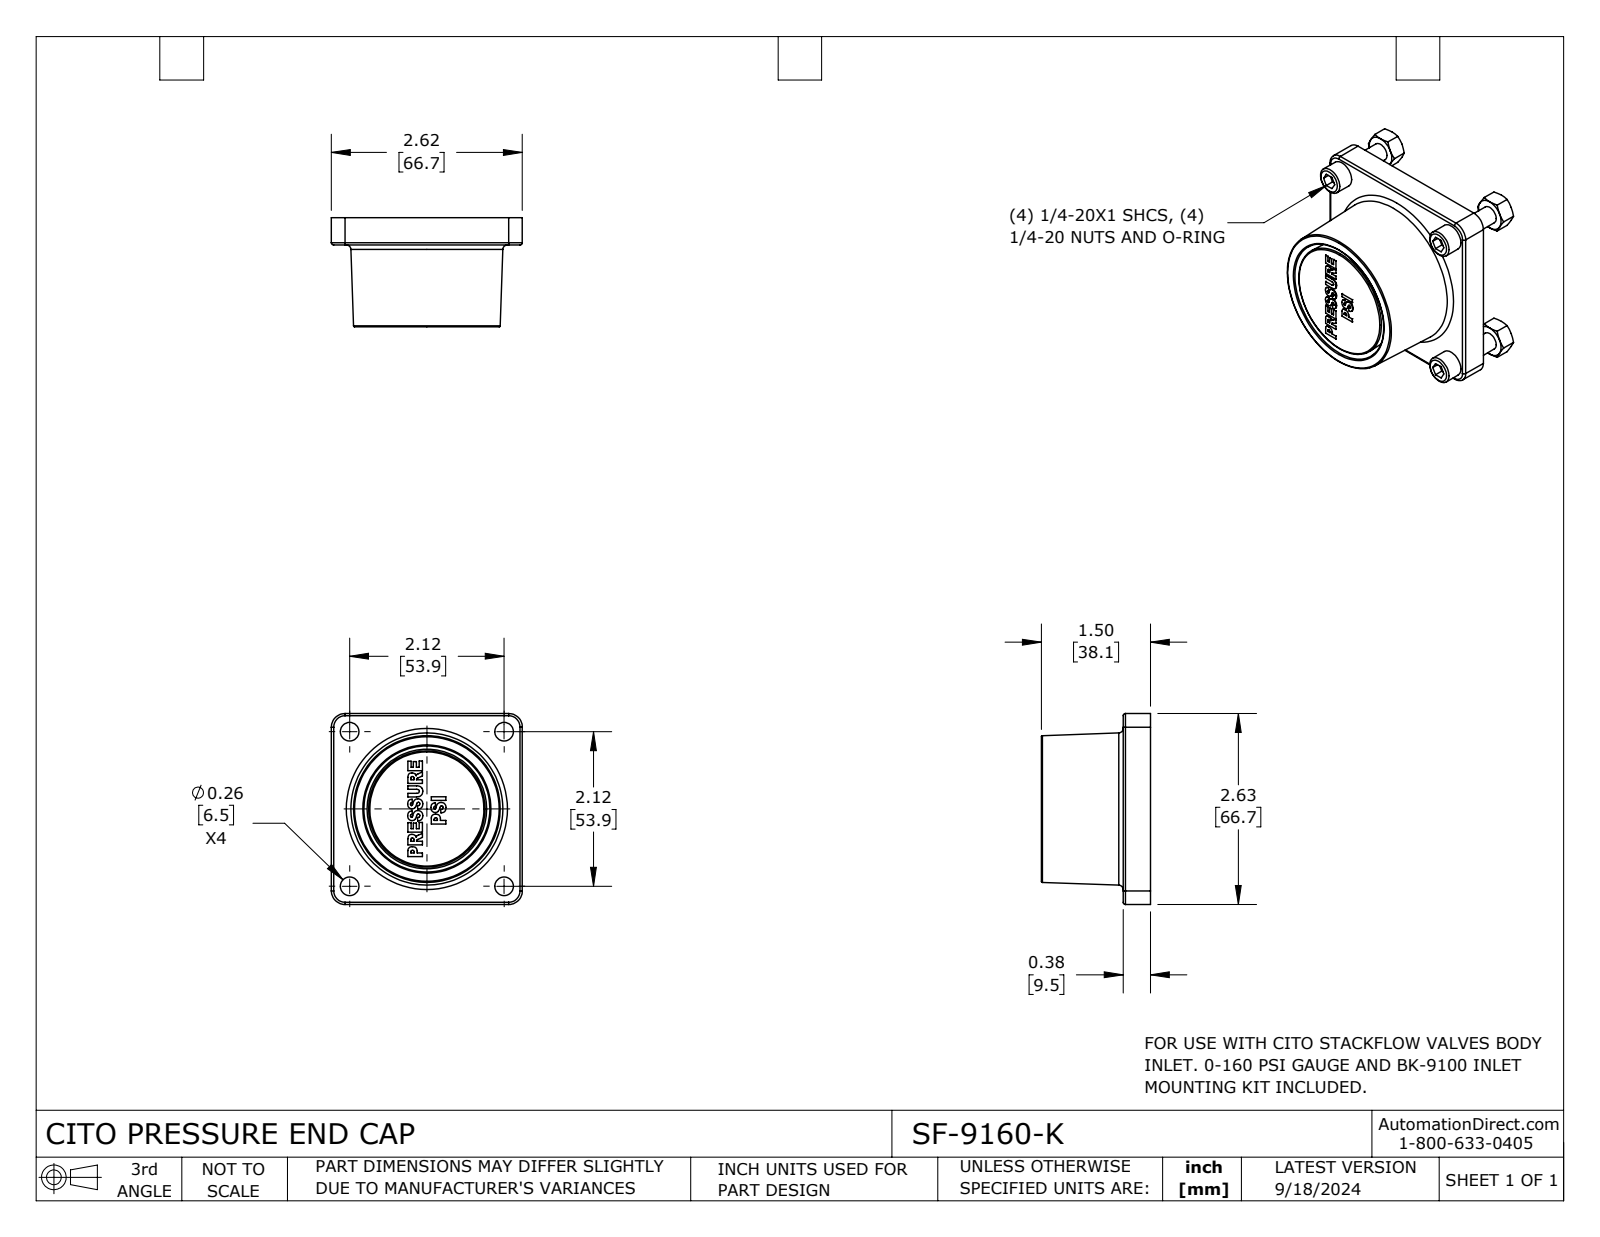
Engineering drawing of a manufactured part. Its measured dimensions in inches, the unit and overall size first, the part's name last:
Units: inches
Overall size (bounding box): 2.63 × 2.625 × 2.125
Round holes (diameter × count): ⌀0.183 ×4, ⌀0.255 ×4, ⌀0.375 ×1
Round bosses / shafts (diameter × count): ⌀0.25 ×4, ⌀0.375 ×2, ⌀0.375 ×2
Partial cylindrical surfaces — rounded edges, fillets, slot ends (radius × count): R0.031 ×4, R0.187 ×2, R0.188 ×2
Main face-to-face distances: 0.375, 1, 1.111, 0.2, 0.175, 1.485, 1.285, 0.485, 0.285, 0.111
Hole centre spacings: 1.502, 2.124, 3.003
Volume: 5.639 in³ · Surface area: 49.23 in²
Bodies: 22 solids, 407 faces (182 planar, 42 cylindrical, 183 other)
Part name (STEP PRODUCT): SF-9160-K
STEP written by: SolidWorks 2023 (CONFIG_CONTROL_DESIGN)
